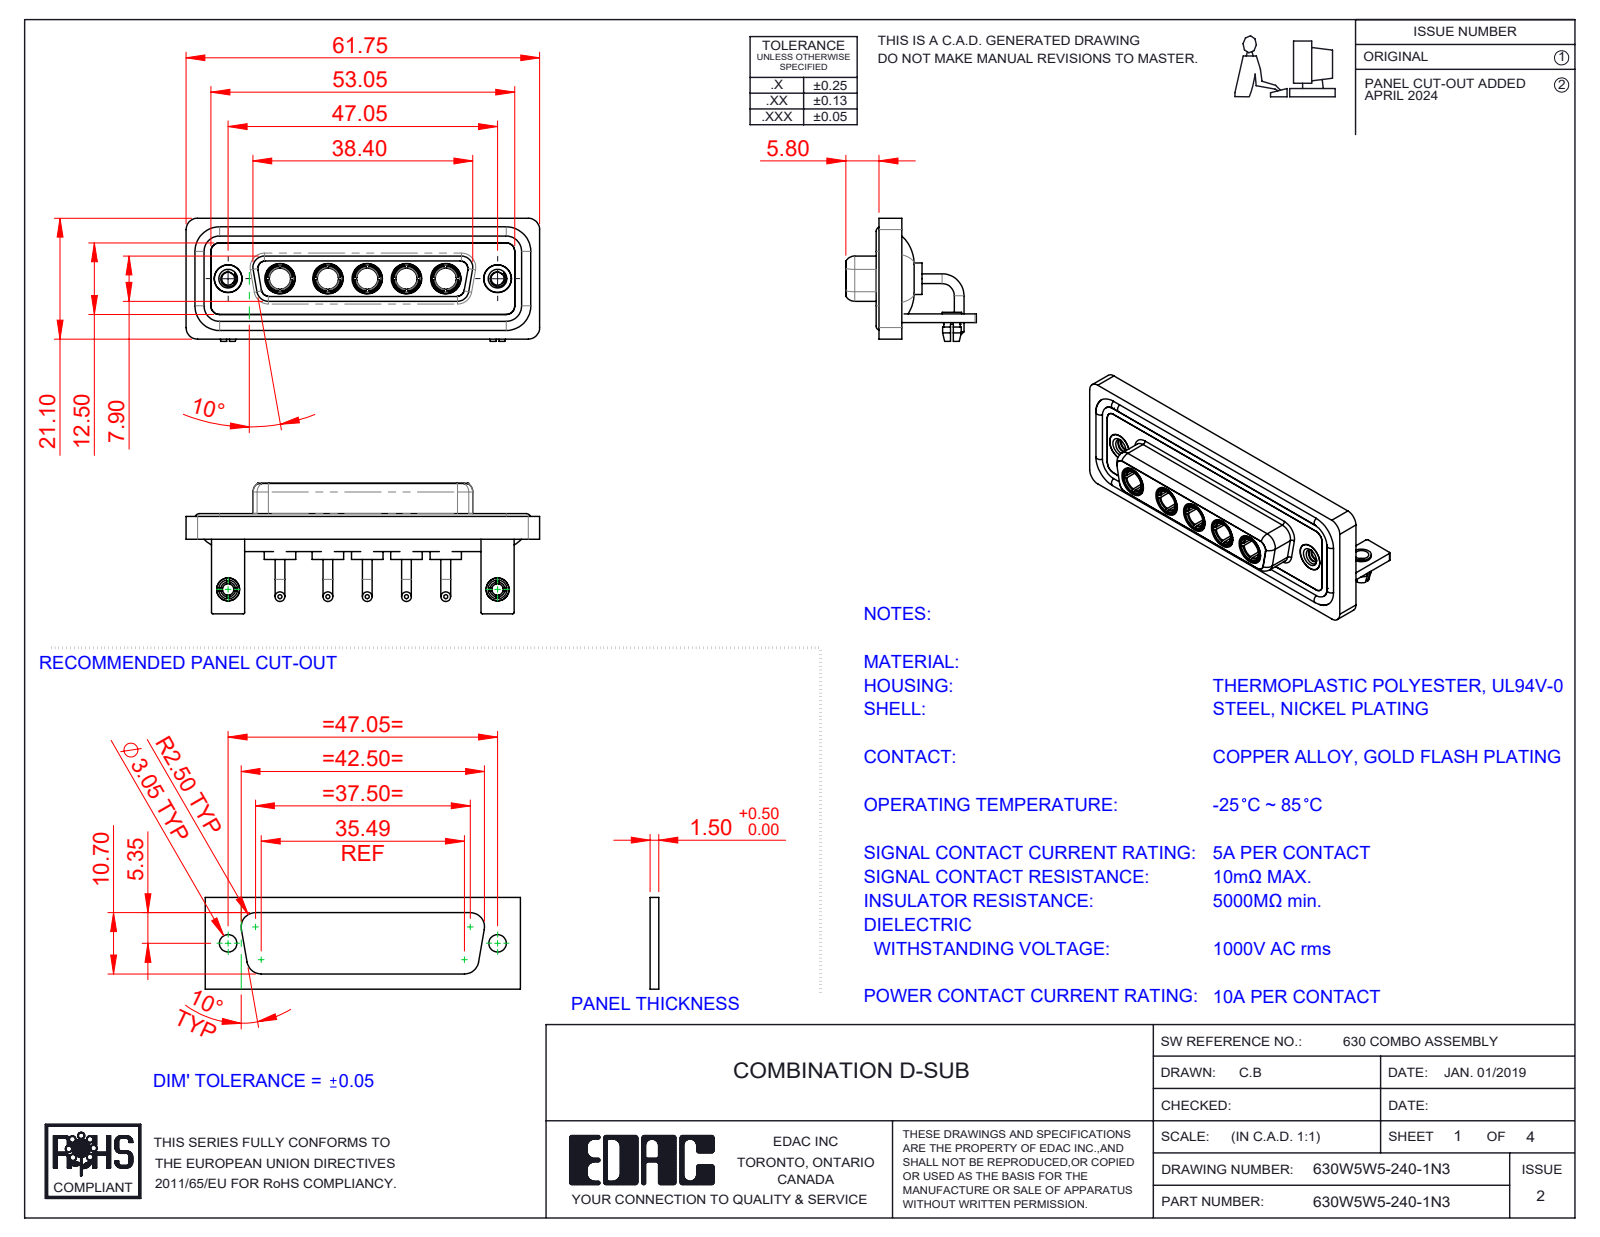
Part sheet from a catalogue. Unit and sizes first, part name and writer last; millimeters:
Units: millimetres
Overall size (bounding box): 61.75 × 22.8 × 21.5
Round holes (diameter × count): ⌀4.85 ×7, ⌀3.7 ×5, ⌀5.3 ×5, ⌀2 ×2, ⌀2.26 ×2, ⌀2.5 ×2, ⌀3.2 ×2, ⌀4 ×2, ⌀4.05 ×2, ⌀5 ×2
Round bosses / shafts (diameter × count): ⌀1.7 ×10, ⌀5.5 ×5, ⌀5.2 ×5, ⌀4.96 ×5, ⌀4.75 ×5, ⌀3.75 ×5, ⌀1.6 ×4, ⌀4.95 ×2
Partial cylindrical surfaces — rounded edges, fillets, slot ends (radius × count): R2 ×19, R1.5 ×18, R0.25 ×16, R1.35 ×8, R1.6 ×8, R0.5 ×5, R2.1 ×5, R0.6 ×4
Main face-to-face distances: 0.4, 1.8, 1.5, 2.9, 3.7, 4.1, 1.1, 1.4, 1.6, 2.5
Hole centre spacings: 6.86, 9.04, 38.01, 47.05, 6.87, 8.38, 13.72, 13.73
Volume: 8 549 mm³ · Surface area: 14 505 mm²
Bodies: 21 solids, 916 faces (318 planar, 369 cylindrical, 229 other)
Part name (STEP PRODUCT): 630Combo Stabilizer Bracket_50 Contacts; 630Combo Board Lock_50 Contacts; 630Combo Housing_5W5; 630W5W5-140-1N3 (+5 more)
STEP written by: SolidWorks 2023 (CONFIG_CONTROL_DESIGN)
